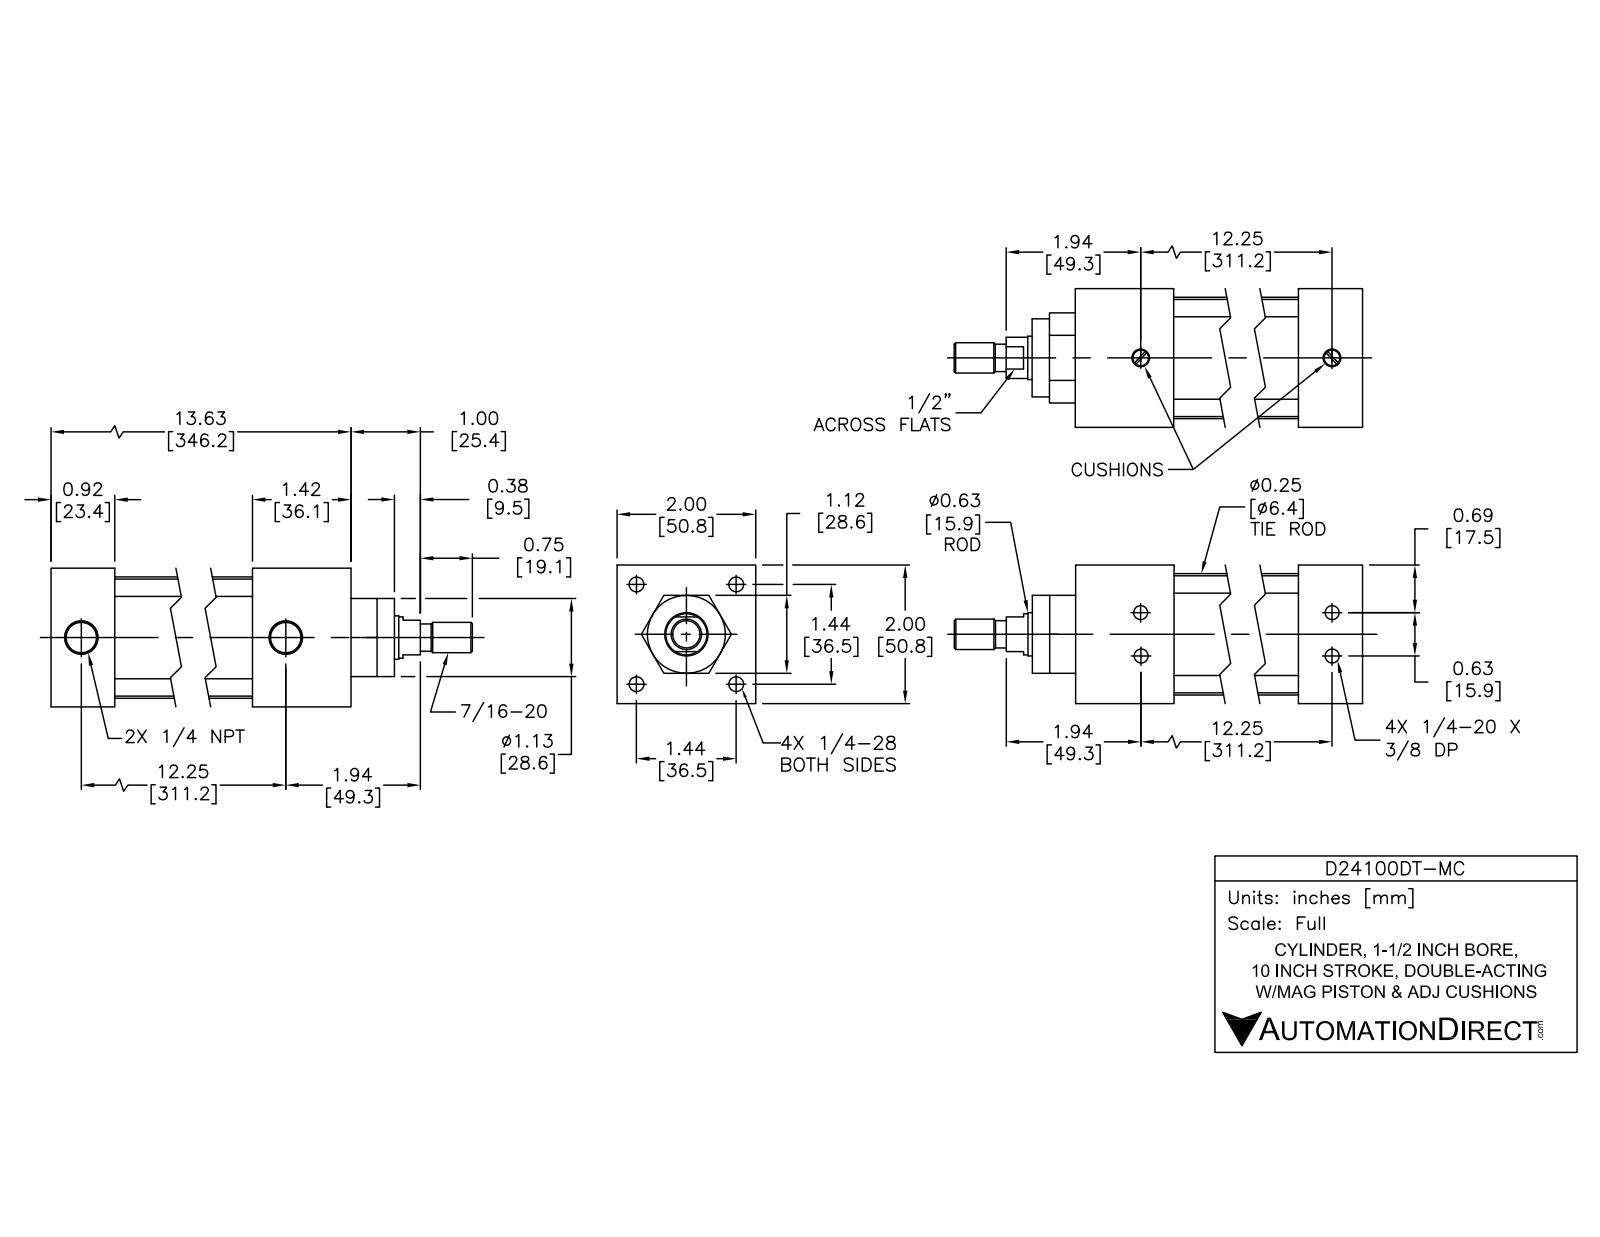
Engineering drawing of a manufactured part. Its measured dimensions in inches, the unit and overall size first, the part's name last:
Units: inches
Overall size (bounding box): 15.371 × 2 × 2
Round holes (diameter × count): ⌀0.196 ×4, ⌀0.211 ×4, ⌀0.281 ×4, ⌀0.406 ×4, ⌀0.297 ×2, ⌀0.477 ×2, ⌀0.625 ×1, ⌀0.628 ×1, ⌀1.5 ×1
Round bosses / shafts (diameter × count): ⌀0.39 ×4, ⌀0.25 ×4, ⌀0.222 ×4, ⌀1.75 ×1, ⌀1.497 ×1, ⌀1.121 ×1, ⌀0.622 ×1, ⌀0.59 ×1
Partial cylindrical surfaces — rounded edges, fillets, slot ends (radius × count): R0.2 ×4
Main face-to-face distances: 2, 13.621, 1.42, 12.201, 12.701, 11.281, 0.92, 1.121, 12.601, 11.181
Hole centre spacings: 0.313, 1.014, 1.434, 0.625, 2.028, 12.247, 12.25, 12.25
Volume: 23.66 in³ · Surface area: 242.6 in²
Bodies: 12 solids, 303 faces (99 planar, 114 cylindrical, 90 other)
Part name (STEP PRODUCT): D24100DT-M PISTON; D24100DT-MC; D24100DT-M BODY
STEP written by: SolidWorks 2015 (AUTOMOTIVE_DESIGN)
